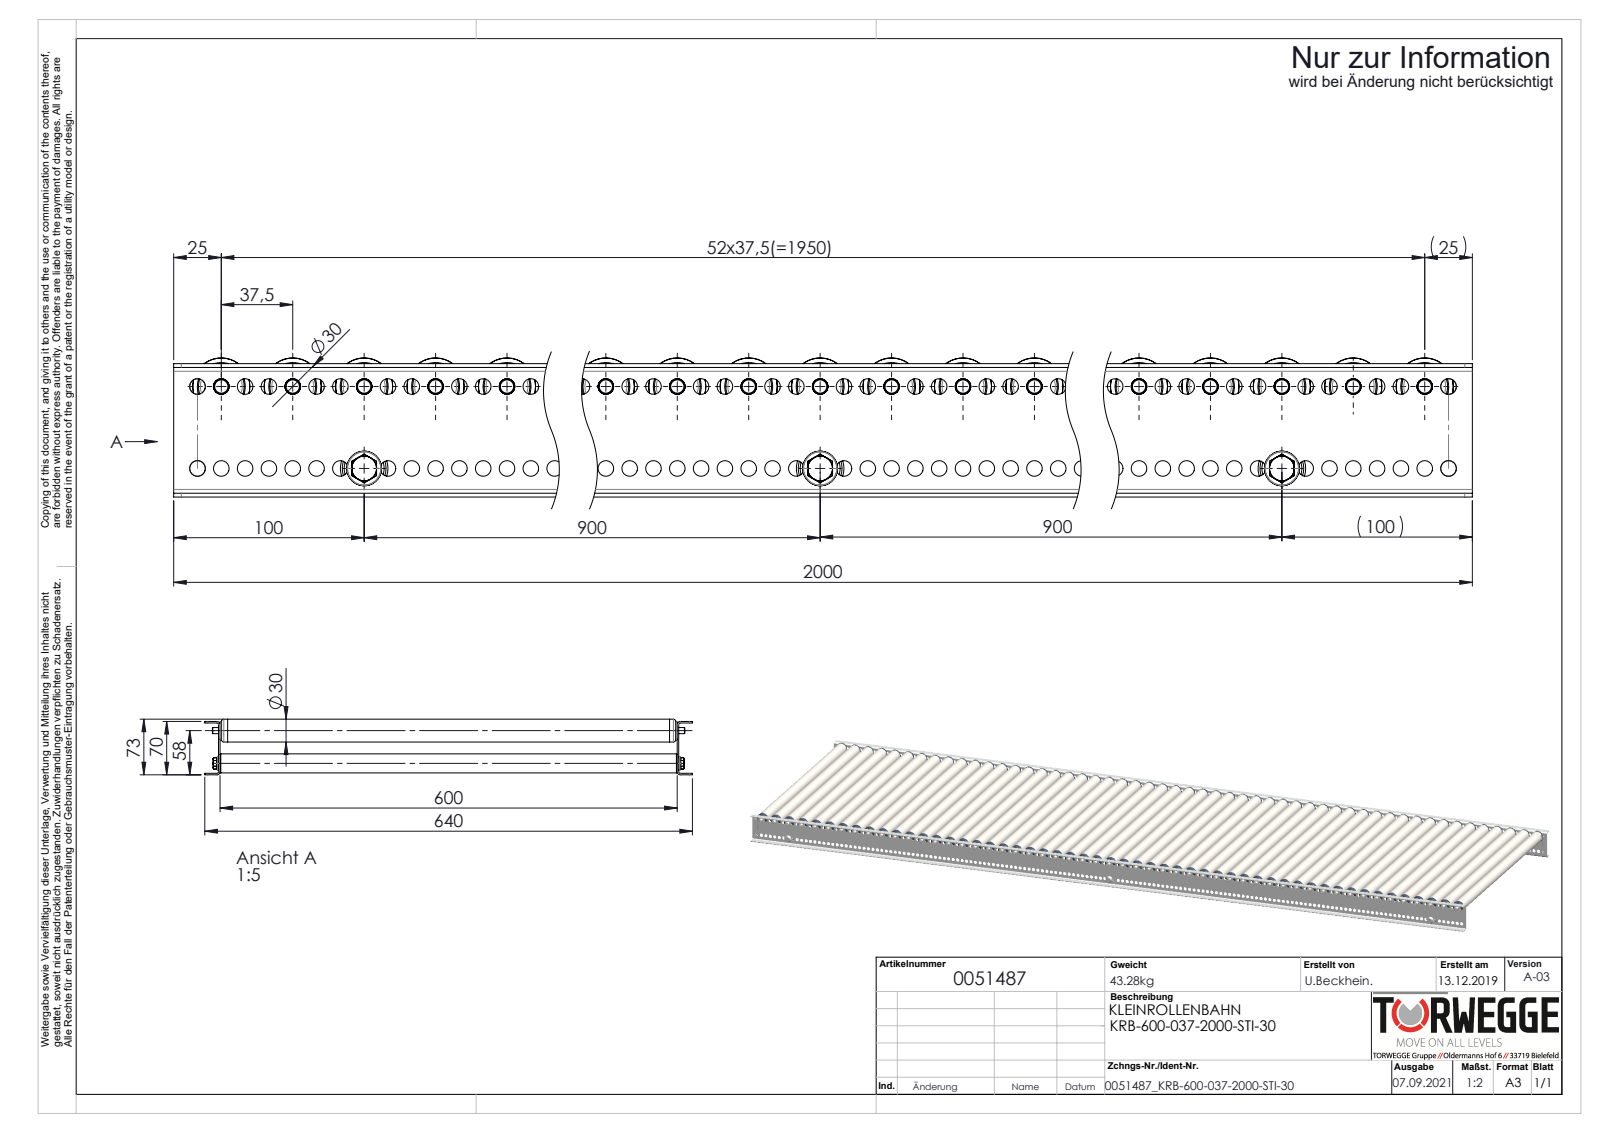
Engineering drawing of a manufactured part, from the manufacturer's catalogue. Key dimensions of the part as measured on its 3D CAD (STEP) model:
Part name (STEP PRODUCT): Profil_KRB-20x70x20x2_KFG_S100232_U-PROFIL-20-70-20-2-KRB-30-L=2000; 0040250_DRUCK-FEDER-8mm; KUT50-30x1,5-STI-A8-FA_KFG_S100907_KUT50-30x1,5-STI-A8-FA-EL=600; 0039778-Achse-ST-Ø08-KFG_AL620-G-FA (+6 more)
STEP written by: SolidWorks 2020 (AUTOMOTIVE_DESIGN)
Units: millimetres
Bodies: 335 solids, 14068 faces (4402 planar, 5588 cylindrical, 4078 other)
Overall size (bounding box): 2000 × 640 × 73
Volume: 6 875 000 mm³ · Surface area: 8 185 000 mm²
Round holes (diameter × count): ⌀8.2 ×318, ⌀8 ×53, ⌀8.1 ×53, ⌀23.2 ×53, ⌀25.2 ×53, ⌀27 ×53, ⌀6.8 ×3, ⌀21 ×3
Round bosses / shafts (diameter × count): ⌀30 ×53, ⌀29.9 ×53, ⌀27.1 ×53, ⌀26.8 ×53, ⌀24 ×53, ⌀14 ×53, ⌀25 ×3, ⌀8 ×3
Partial cylindrical surfaces — rounded edges, fillets, slot ends (radius × count): R5.05 ×53, R4 ×8, R2 ×4
Main face-to-face distances: 2, 602, 600, 68, 604, 70, 66, 10, 590, 20
Hole centre spacings: 12.5, 25, 37.5, 50, 62.5, 75, 87.5, 100
